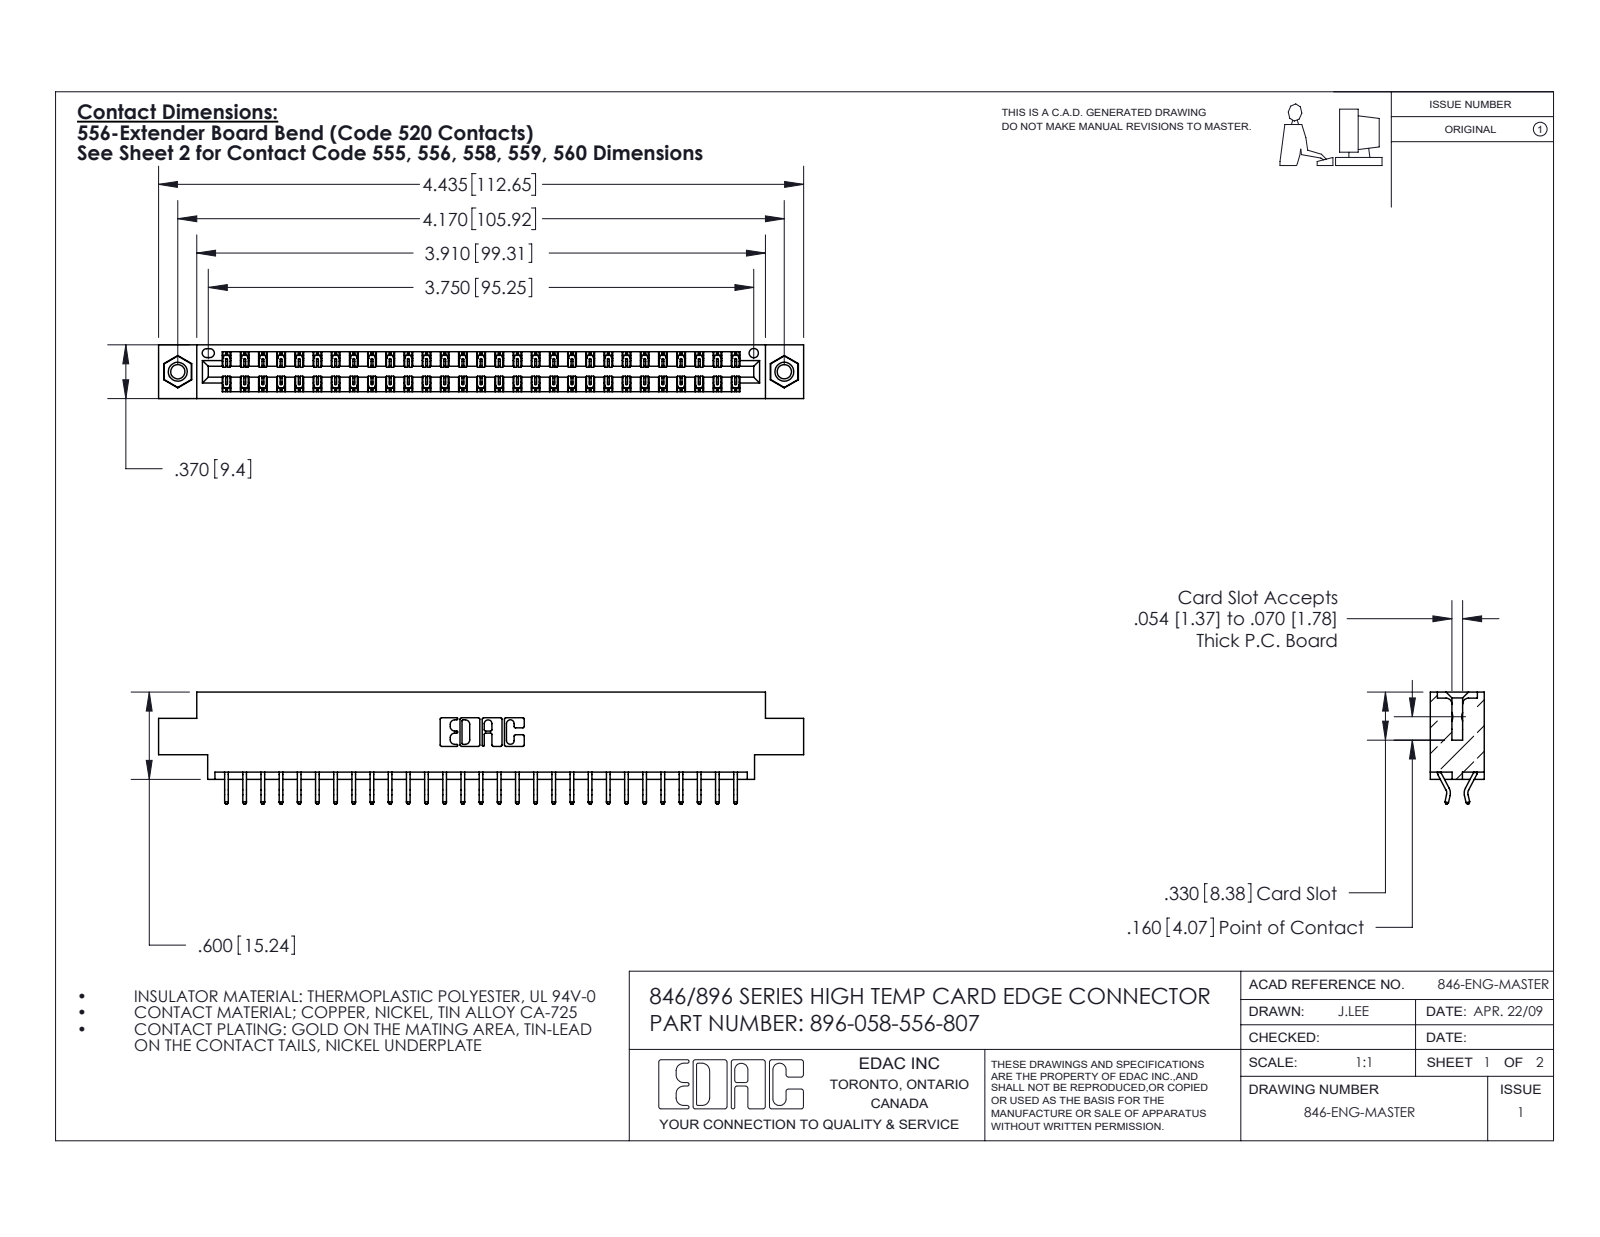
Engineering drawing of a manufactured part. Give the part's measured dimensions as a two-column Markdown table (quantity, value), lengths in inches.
| quantity | value |
| --- | --- |
| part name | 345-292-001_556 Tail; 396-058-556-807; 345-250-001_345-250-005-103; 346 Part_0.170 Offset - 0.156 Dia-TI |
| STEP written by | SolidWorks 2016 (CONFIG_CONTROL_DESIGN) |
| units | inches |
| bodies | 61 solids, 3550 faces (2374 planar, 1160 cylindrical, 16 other) |
| overall size | 4.435 × 0.77 × 0.37 |
| volume | 0.654 in³ |
| surface area | 22.76 in² |
| round holes (diameter × count) | 0.098 × 2, 0.125 × 2, 0.156 × 2, 0.064 × 1 |
| round bosses / shafts (diameter × count) | 0.155 × 2 |
| partial cylindrical surfaces (radius × count) | 0.006 × 87, 0.01 × 22, 0.007 × 6, 0.031 × 6, 0.026 × 3, 0.01 × 2, 0.014 × 2, 0.022 × 2 |
| main face-to-face distances | 0.048, 0.322, 0.37, 0.25, 0.025, 0.072, 0.298, 0.275, 0.222, 0.148 |
| hole center spacings | 0.246, 3.962, 4.17 |
